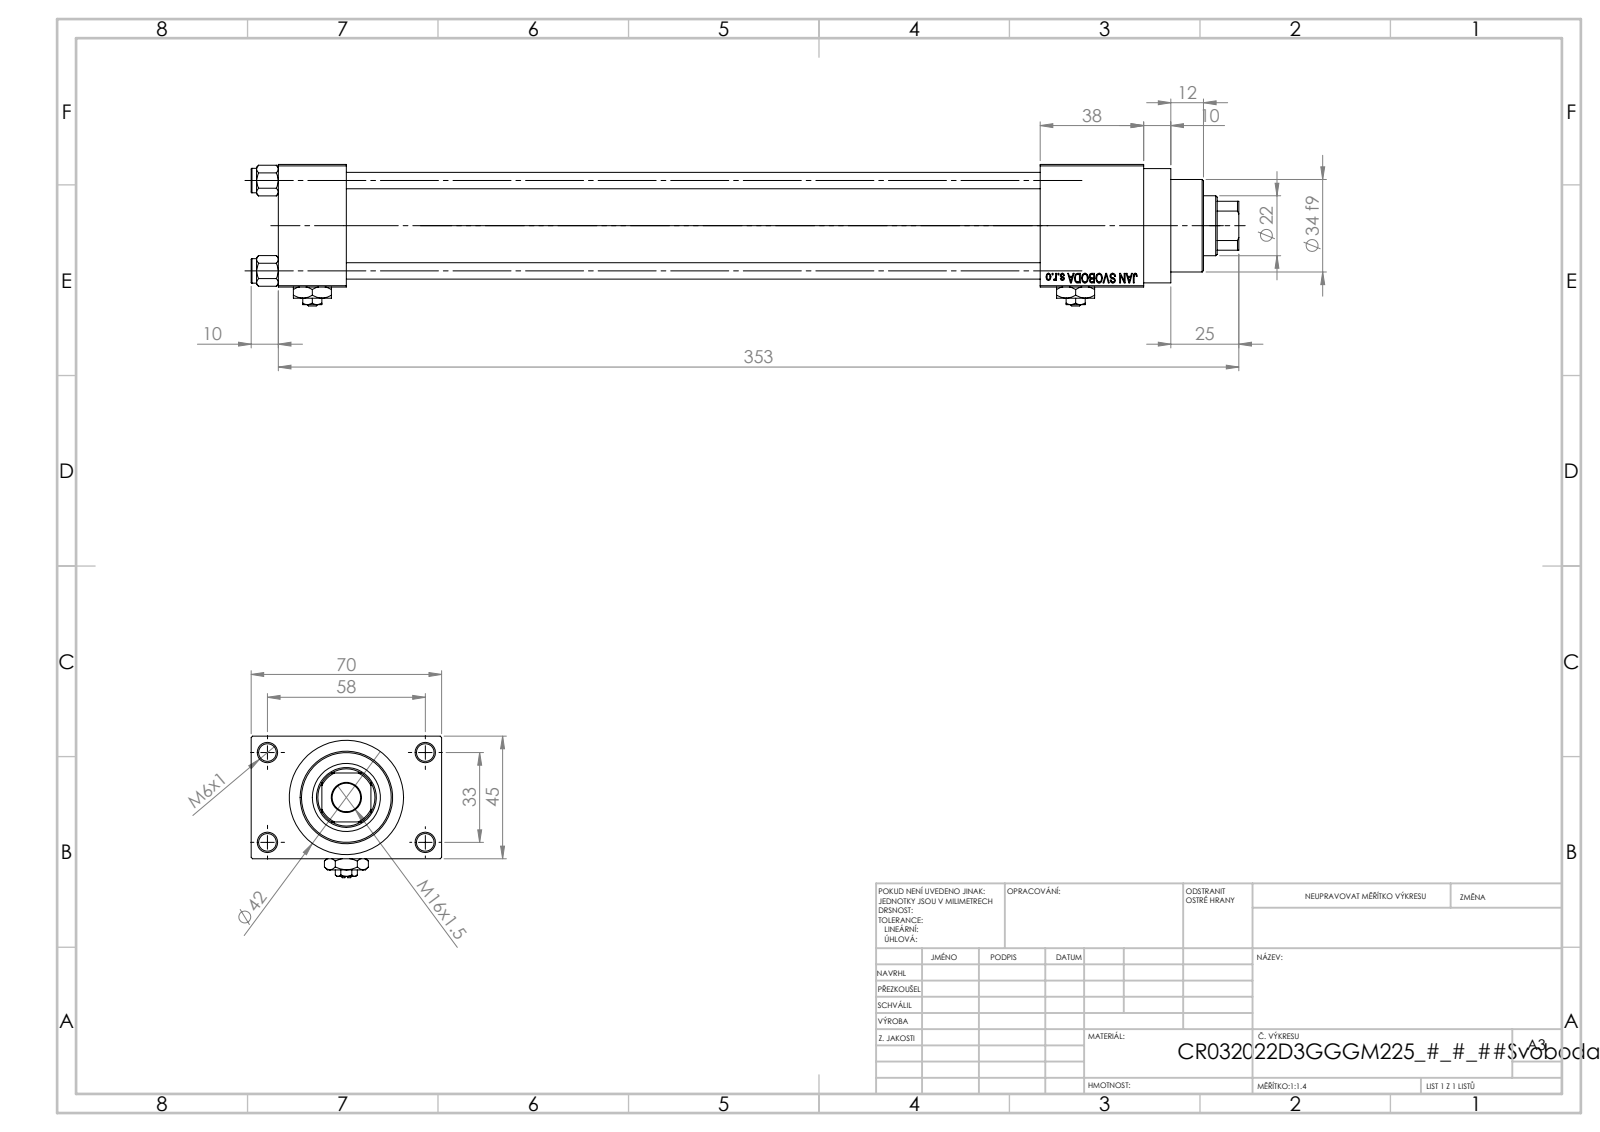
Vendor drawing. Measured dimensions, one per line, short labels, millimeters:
name: V215CR_D_TYCINKA; V215CR_VCP_D; Zatka_pro_OIL_PORT; V215CR_D_Body (+2 more)
written by: SolidWorks 2019 (CONFIG_CONTROL_DESIGN)
unit: mm
bodies: 13 solids, 1202 faces (542 planar, 100 cylindrical, 560 other)
size: 363 × 70 × 52
volume: 412 102 mm³; area: 155 907 mm²
holes: 4× ⌀6, 4× ⌀6.5, 2× ⌀7, 2× ⌀13.16, 2× ⌀20, 1× ⌀10.5, 1× ⌀22, 1× ⌀24, 1× ⌀25, 1× ⌀32, 1× ⌀33
bosses: 4× ⌀9, 1× ⌀42, 1× ⌀38, 1× ⌀34
rounds: 1× R10.5
face distances: 45, 25, 12.5, 57.5, 255, 280, 293, 38, 70, 318
hole spacings: 12.4, 23.48, 33.2, 33.37, 35.35, 45.6, 56.35, 33
